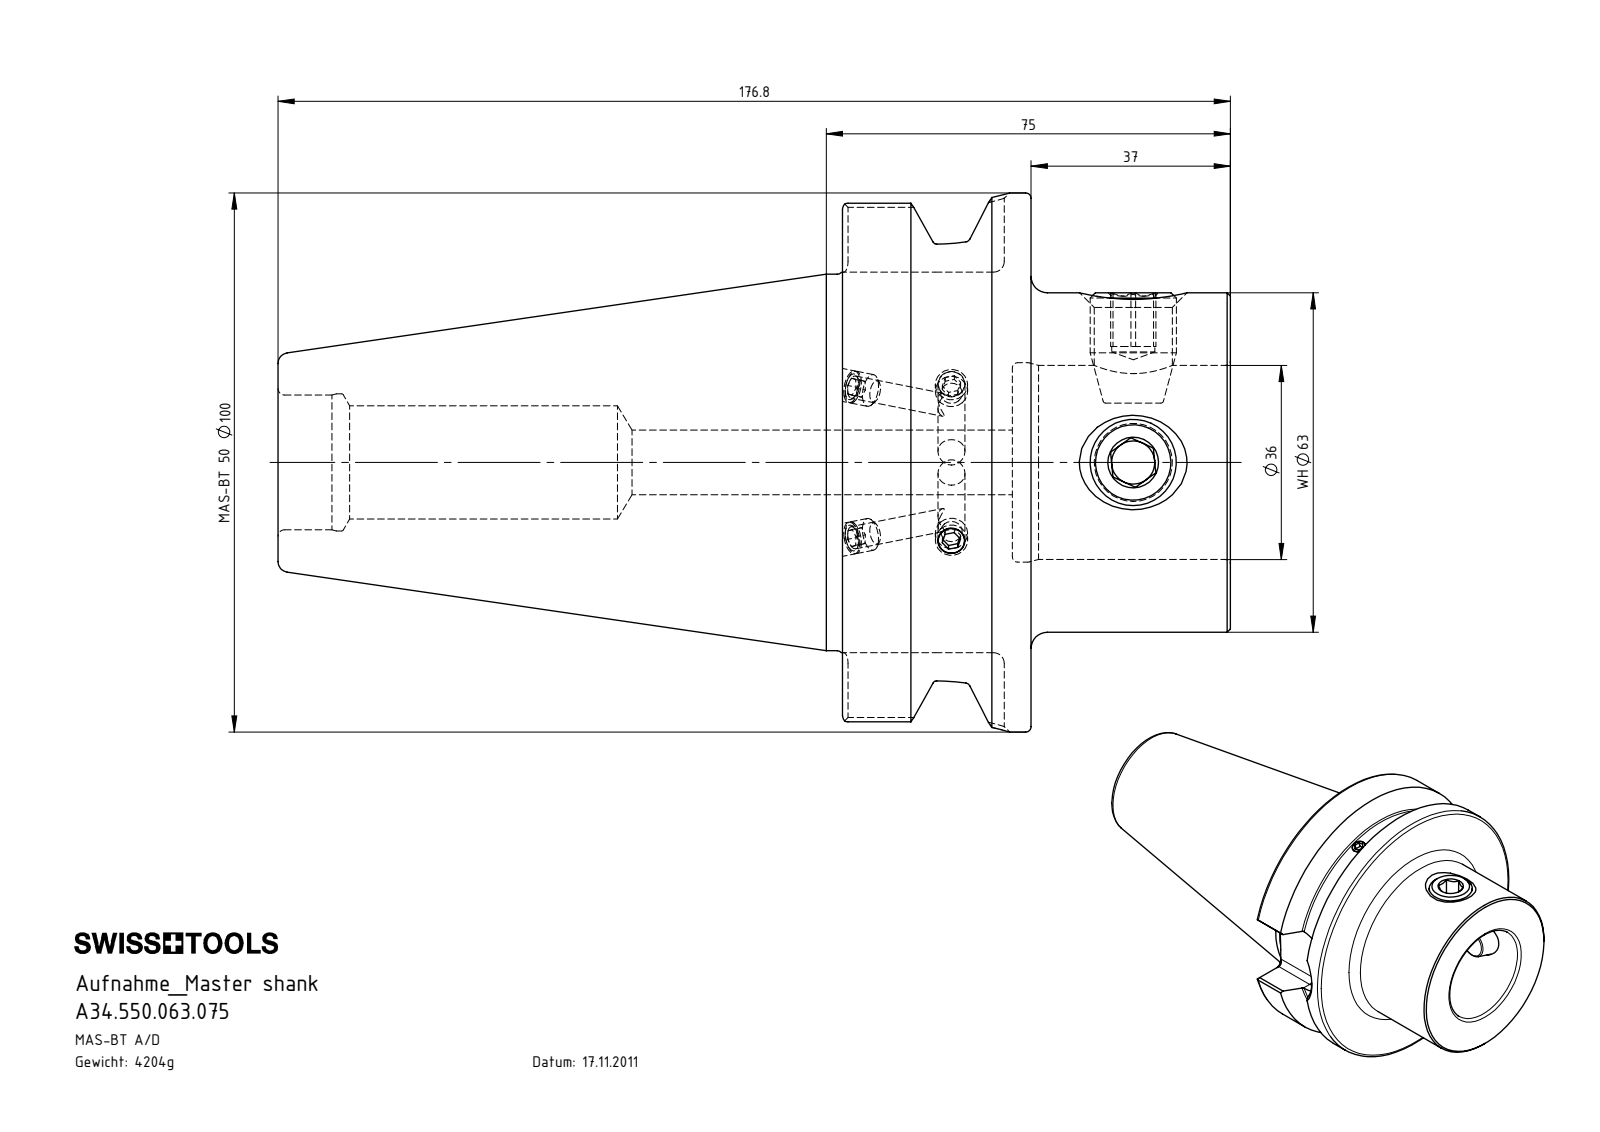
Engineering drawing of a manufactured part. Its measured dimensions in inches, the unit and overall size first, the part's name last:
Units: inches
Overall size (bounding box): 6.961 × 3.937 × 3.937
Round holes (diameter × count): ⌀0.165 ×2, ⌀0.236 ×2, ⌀0.315 ×2, ⌀0.571 ×2, ⌀0.197 ×1, ⌀0.472 ×1, ⌀0.827 ×1, ⌀0.984 ×1, ⌀1.002 ×1, ⌀1.417 ×1, ⌀1.457 ×1
Round bosses / shafts (diameter × count): ⌀0.63 ×2, ⌀0.236 ×2, ⌀3.937 ×1, ⌀3.346 ×1, ⌀2.75 ×1, ⌀2.48 ×1
Partial cylindrical surfaces — rounded edges, fillets, slot ends (radius × count): R0.079 ×8, R0.506 ×1
Main face-to-face distances: 1.378, 2.835, 1.457, 1.24, 0.138, 1.594, 2.78, 4.126, 5.366, 5.504
Volume: 32.72 in³ · Surface area: 106.1 in²
Bodies: 7 solids, 240 faces (84 planar, 65 cylindrical, 91 other)
Part name (STEP PRODUCT): ISO 4026 - M6 x 5_PreviewCfg; BB5-WH6.K01.075; WH6-ER1.001.021; BB5-WH6.K01.075_B
STEP written by: SolidWorks 2015 (AUTOMOTIVE_DESIGN)
